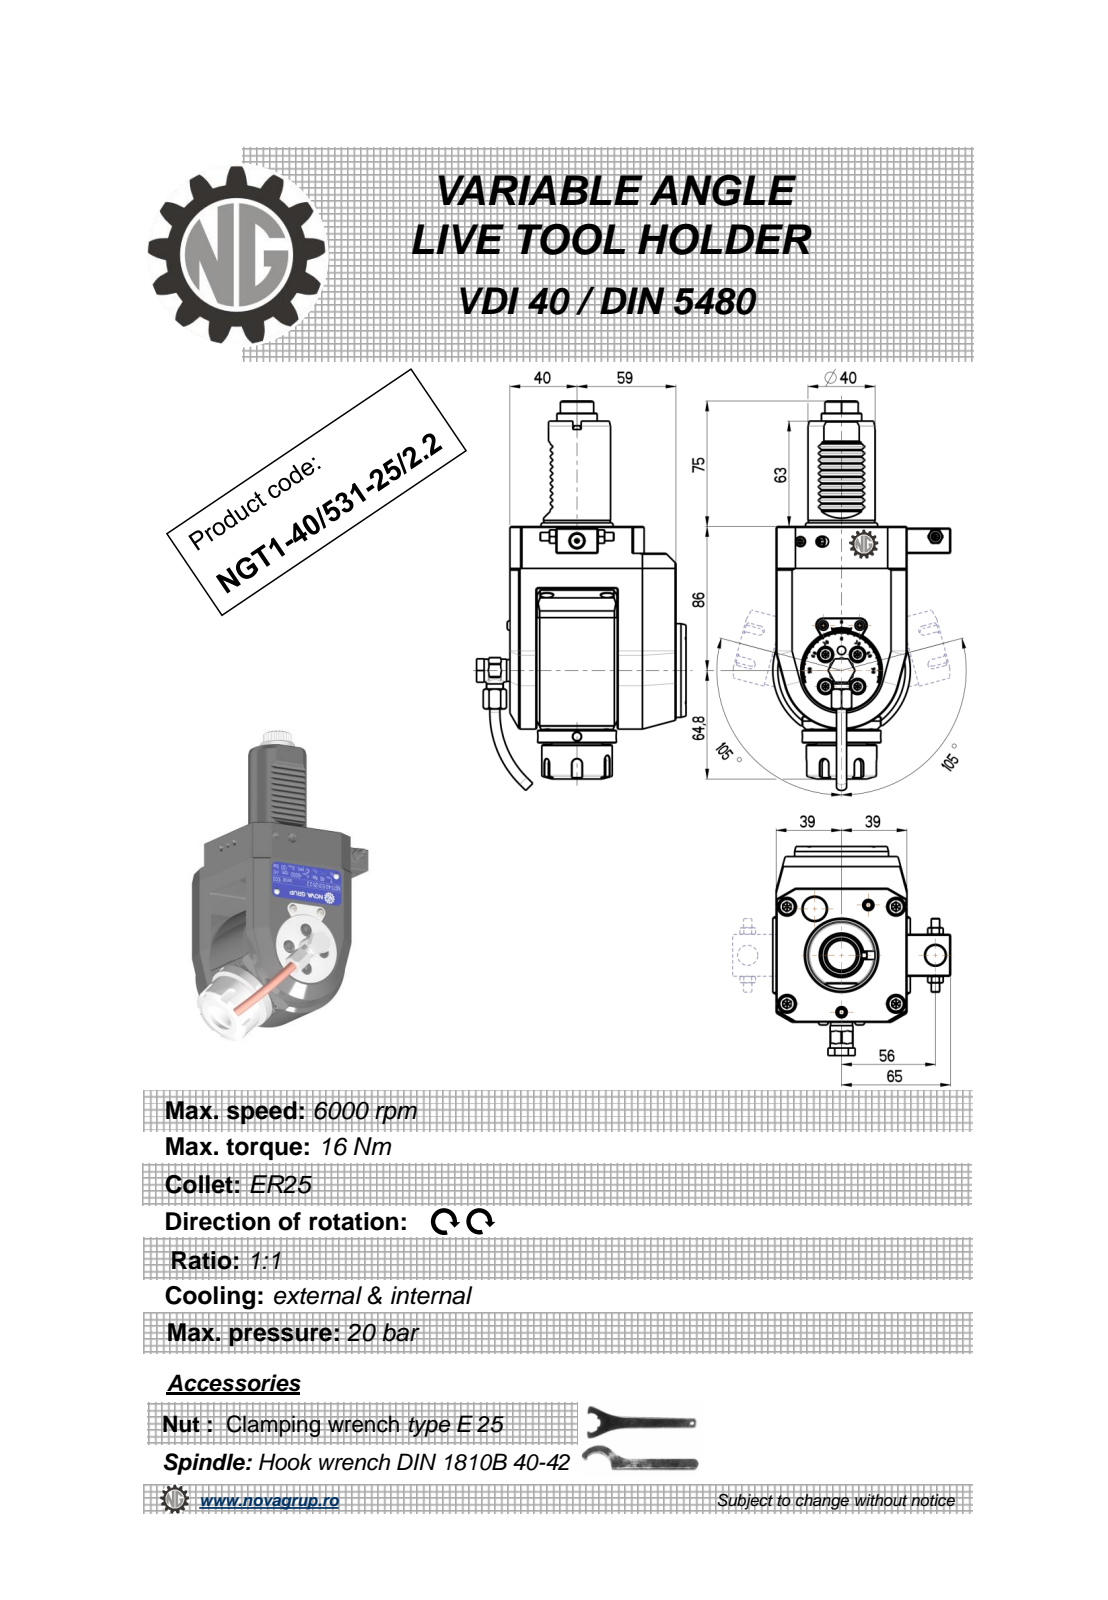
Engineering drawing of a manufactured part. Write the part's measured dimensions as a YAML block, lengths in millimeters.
part_name: "NGT1_40_531_25_2_2"
step_written_by: "PRO/ENGINEER BY PARAMETRIC TECHNOLOGY CORPORATION, 2010280 (CONFIG_CONTROL_DESIGN)"
units: millimeters
bodies: {solids: 1, faces: 707, planar: 254, cylindrical: 237, other: 216}
overall_size: [232.67, 124.9, 106]
volume: 938163
surface_area: 84175
round_holes:
  - {diameter: 4, count: 3}
  - {diameter: 5, count: 2}
  - {diameter: 3, count: 1}
  - {diameter: 4.2, count: 1}
  - {diameter: 6.2, count: 1}
  - {diameter: 9, count: 1}
  - {diameter: 9.5, count: 1}
  - {diameter: 11, count: 1}
  - {diameter: 12, count: 1}
  - {diameter: 20.3, count: 1}
round_bosses_or_shafts:
  - {diameter: 10, count: 2}
  - {diameter: 6, count: 2}
  - {diameter: 5.7, count: 2}
  - {diameter: 56, count: 1}
  - {diameter: 47, count: 1}
  - {diameter: 42, count: 1}
  - {diameter: 40, count: 1}
  - {diameter: 35, count: 1}
partial_cylinders:
  - {radius: 2.08, count: 48}
  - {radius: 0.26, count: 12}
  - {radius: 0.3, count: 10}
  - {radius: 0.16, count: 6}
  - {radius: 3, count: 5}
  - {radius: 0.5, count: 4}
  - {radius: 1, count: 2}
  - {radius: 10, count: 2}
face_to_face_distances: [16, 37, 99, 78, 64, 6, 105, 21, 41, 1]
hole_center_spacings: [0.4, 39.45, 49, 49.4, 56, 74.41, 74.68, 97.65]
